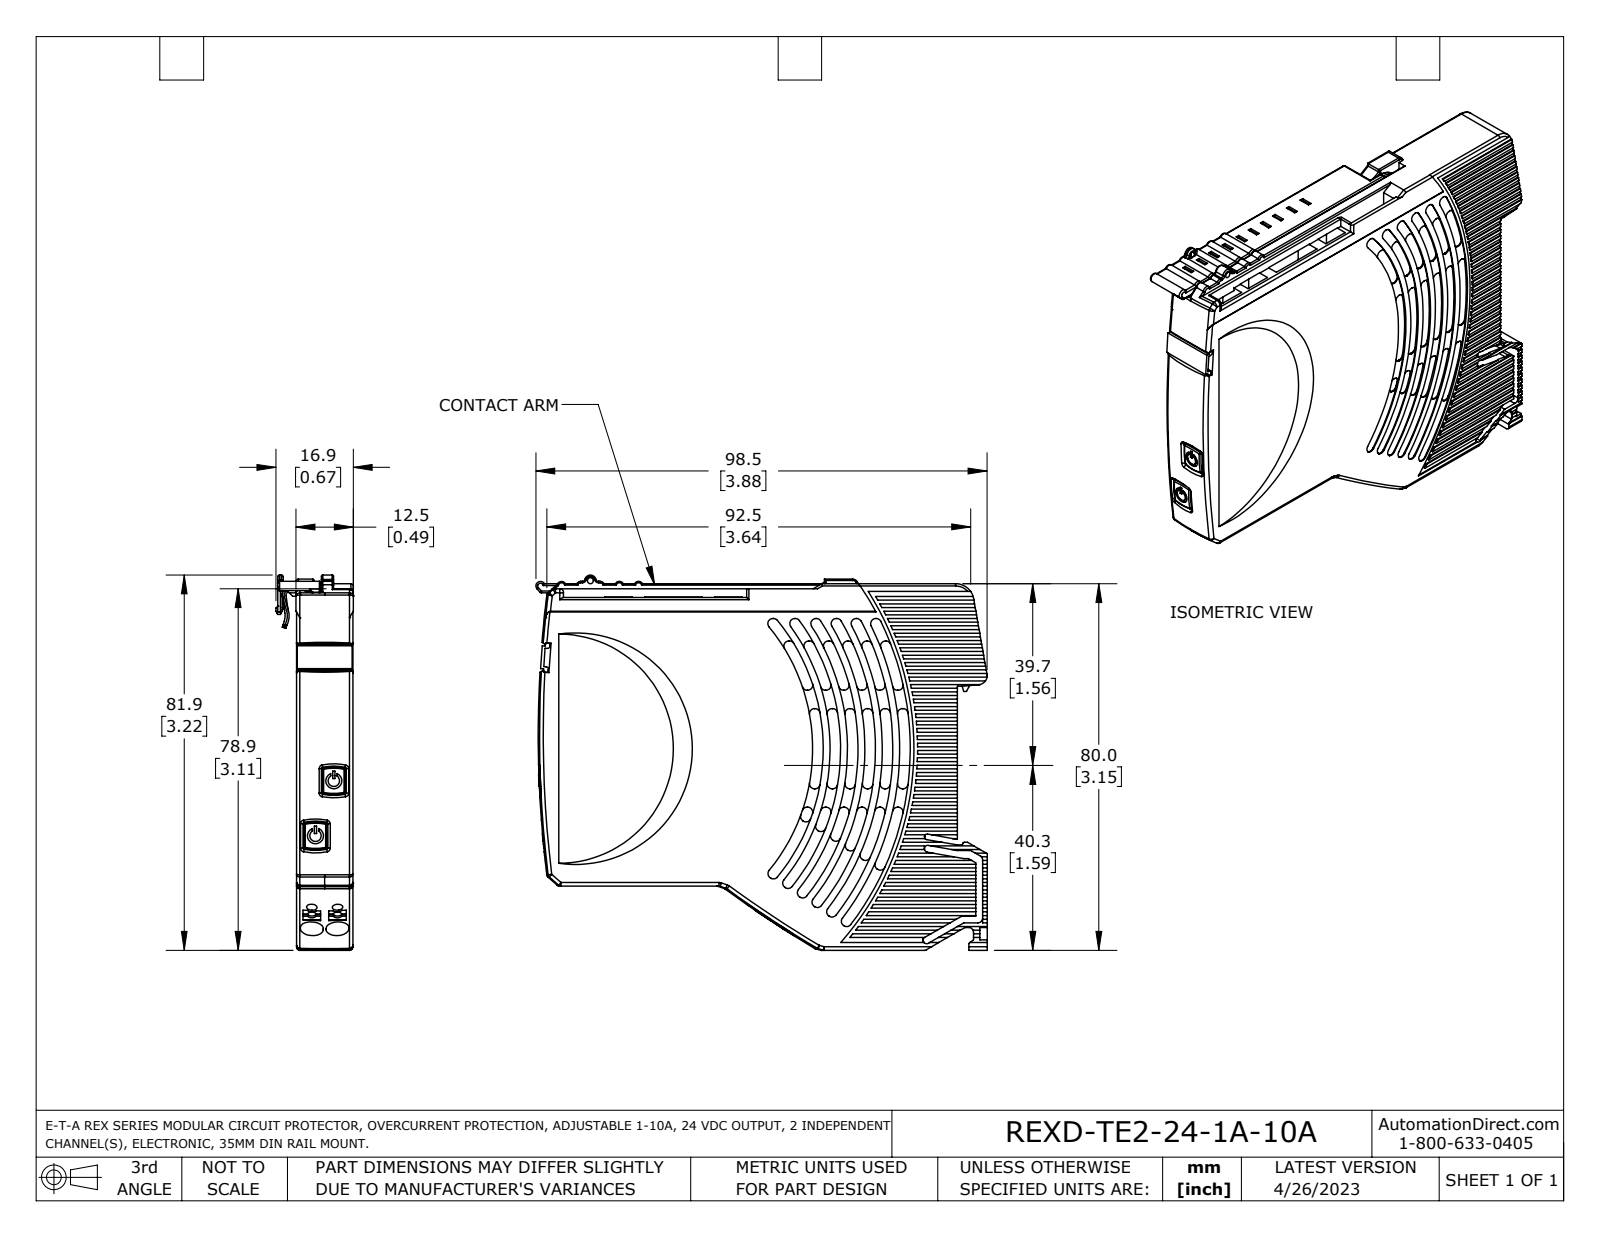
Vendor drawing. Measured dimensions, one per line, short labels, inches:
name: t-rex12d-te2-1xx_ik00
written by: SolidWorks 2021 (AUTOMOTIVE_DESIGN)
unit: in
bodies: 2 solids, 1993 faces (1131 planar, 656 cylindrical, 206 other)
size: 3.878 × 3.224 × 0.665
volume: 4.779 in³; area: 41.84 in²
holes: 2× ⌀0.091, 2× ⌀0.138, 1× ⌀0.051, 1× ⌀0.161
bosses: 2× ⌀0.098, 1× ⌀0.157, 1× ⌀0.079
rounds: 98× R0.043, 69× R0.02, 30× R0.039, 27× R0.016, 24× R0.012, 19× R0.031, 14× R0.008, 8× R0.03
face distances: 0.484, 0.476, 0.469, 0.016, 0.461, 0.059, 0.02, 0.453, 0.039, 0.256
hole spacings: 0.22, 0.498, 2.024
